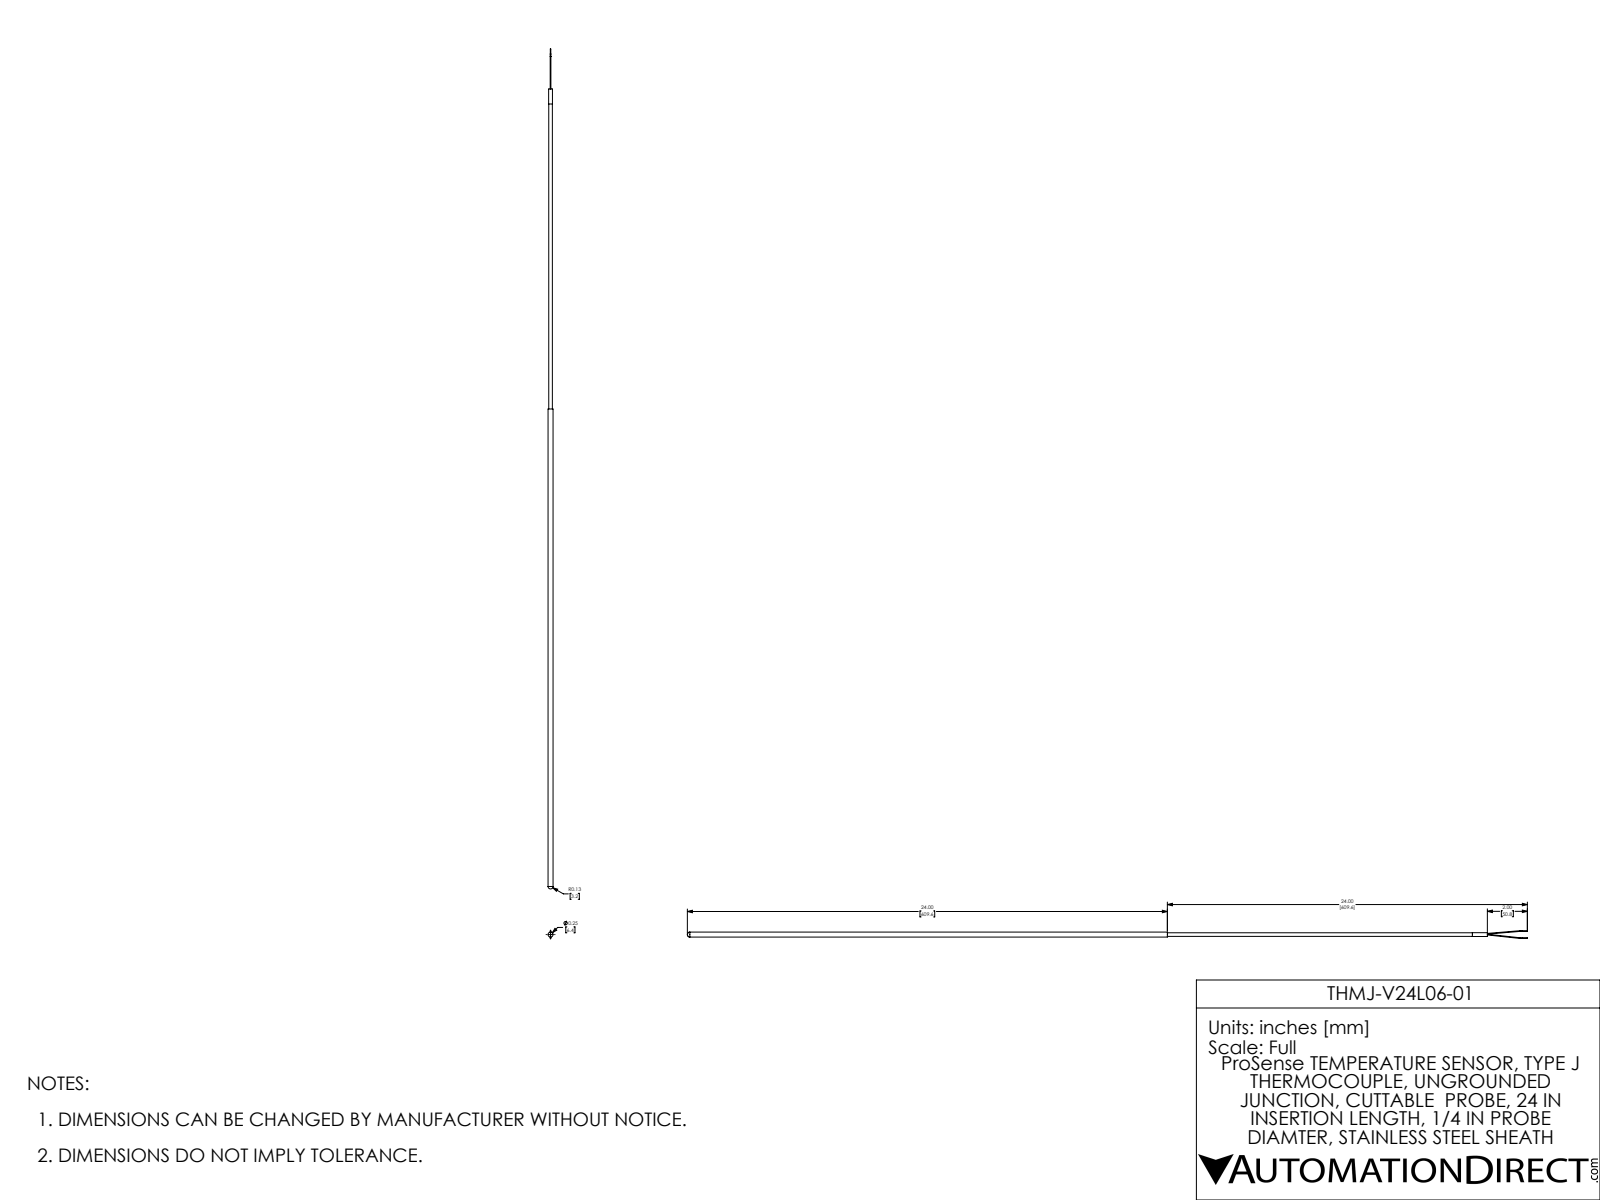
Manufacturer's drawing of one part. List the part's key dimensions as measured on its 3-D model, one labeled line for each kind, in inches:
Part name (STEP PRODUCT): THMJ-V24L06-01
STEP written by: SolidWorks 2017 (AUTOMOTIVE_DESIGN)
Units: inches
Bodies: 4 solids, 33 faces (10 planar, 18 cylindrical, 5 other)
Overall size (bounding box): 41.995 × 0.386 × 0.25
Volume: 1.593 in³ · Surface area: 28.9 in²
Round bosses / shafts (diameter × count): ⌀0.035 ×4, ⌀0.025 ×2, ⌀0.25 ×1, ⌀0.19 ×1, ⌀0.18 ×1
Main face-to-face distances: 16, 2, 0.75, 15.25, 1.25, 14, 2.75, 4, 18, 0.25
